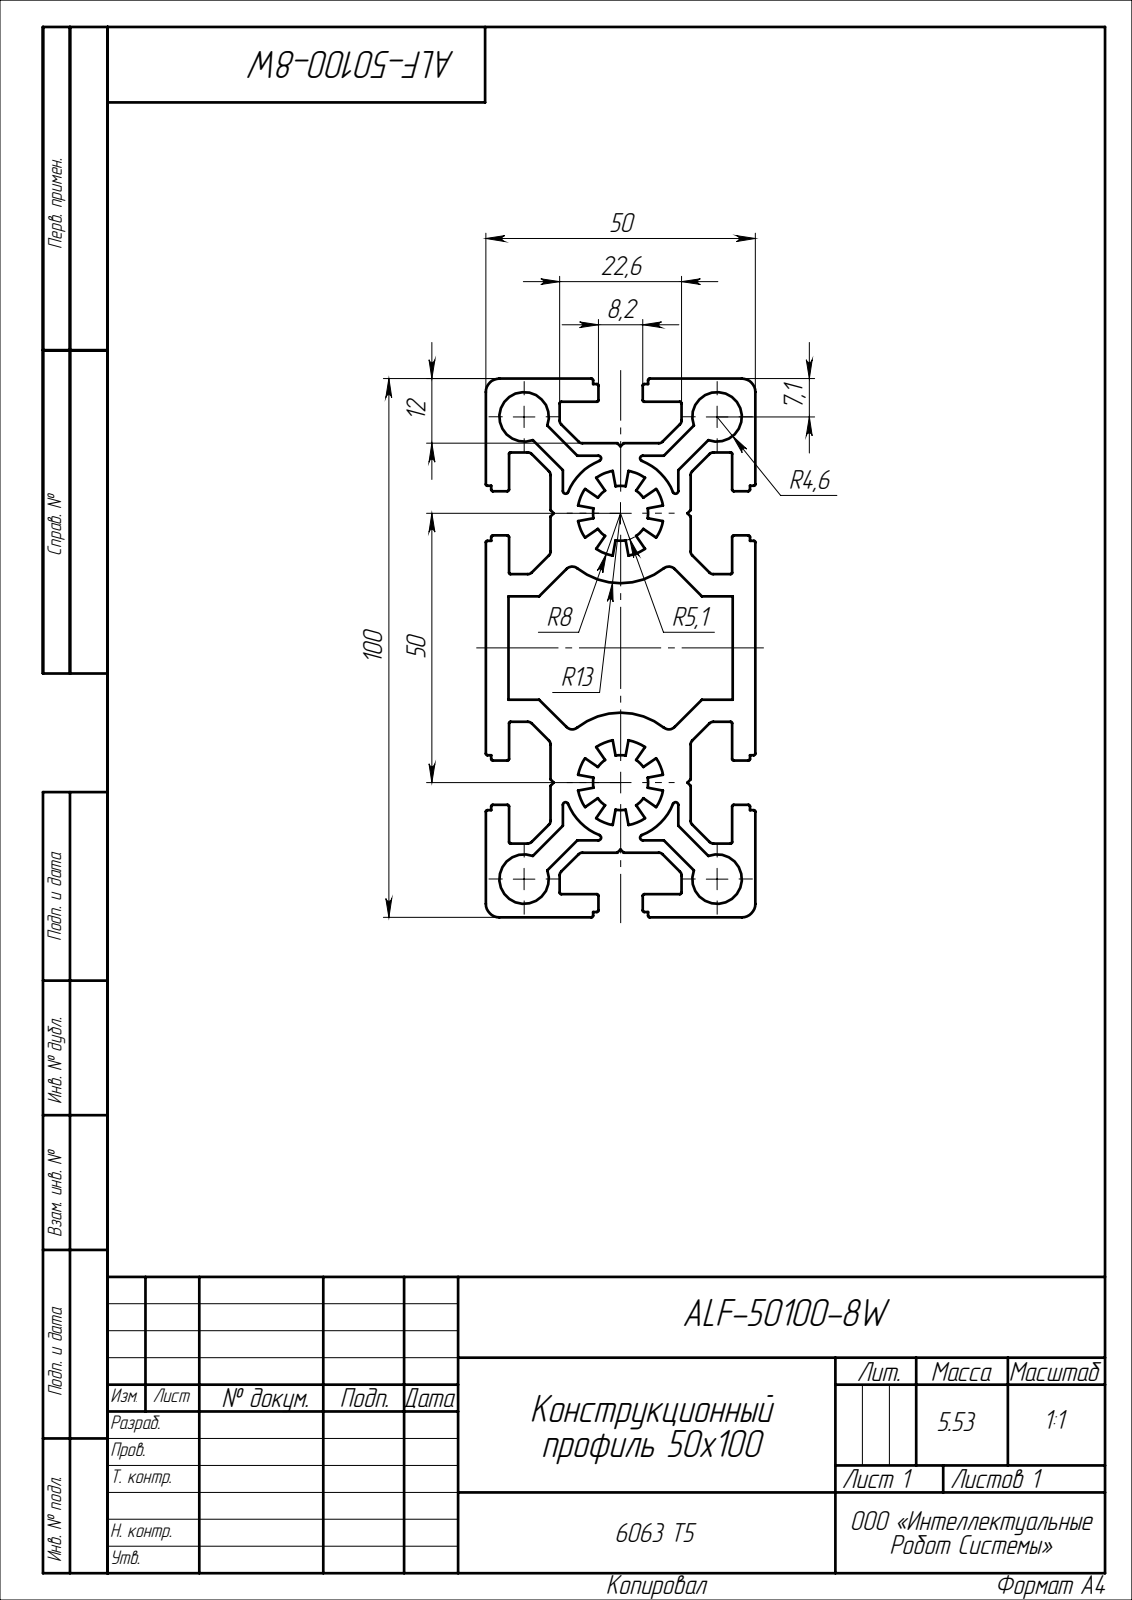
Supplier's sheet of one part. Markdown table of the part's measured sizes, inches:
| quantity | value |
| --- | --- |
| part name | ALF-50100-8W |
| STEP written by | SolidWorks 2022 (CONFIG_CONTROL_DESIGN) |
| units | inches |
| bodies | 1 solid, 308 faces (166 planar, 142 cylindrical, 0 other) |
| overall size | 39.37 × 3.937 × 1.969 |
| volume | 125.5 in³ |
| surface area | 1 758 in² |
| round holes (diameter × count) | 0.362 × 4 |
| partial cylindrical surfaces (radius × count) | 0.012 × 48, 0.039 × 24, 0.02 × 8, 0.059 × 4, 0.098 × 4, 0.201 × 2, 0.315 × 2, 0.413 × 2 |
| main face-to-face distances | 1.969, 0.169, 0.472, 0.303, 1.392, 1.799, 1.496, 1.327, 0.228, 0.078 |
| hole center spacings | 1.409, 3.378, 3.66 |
